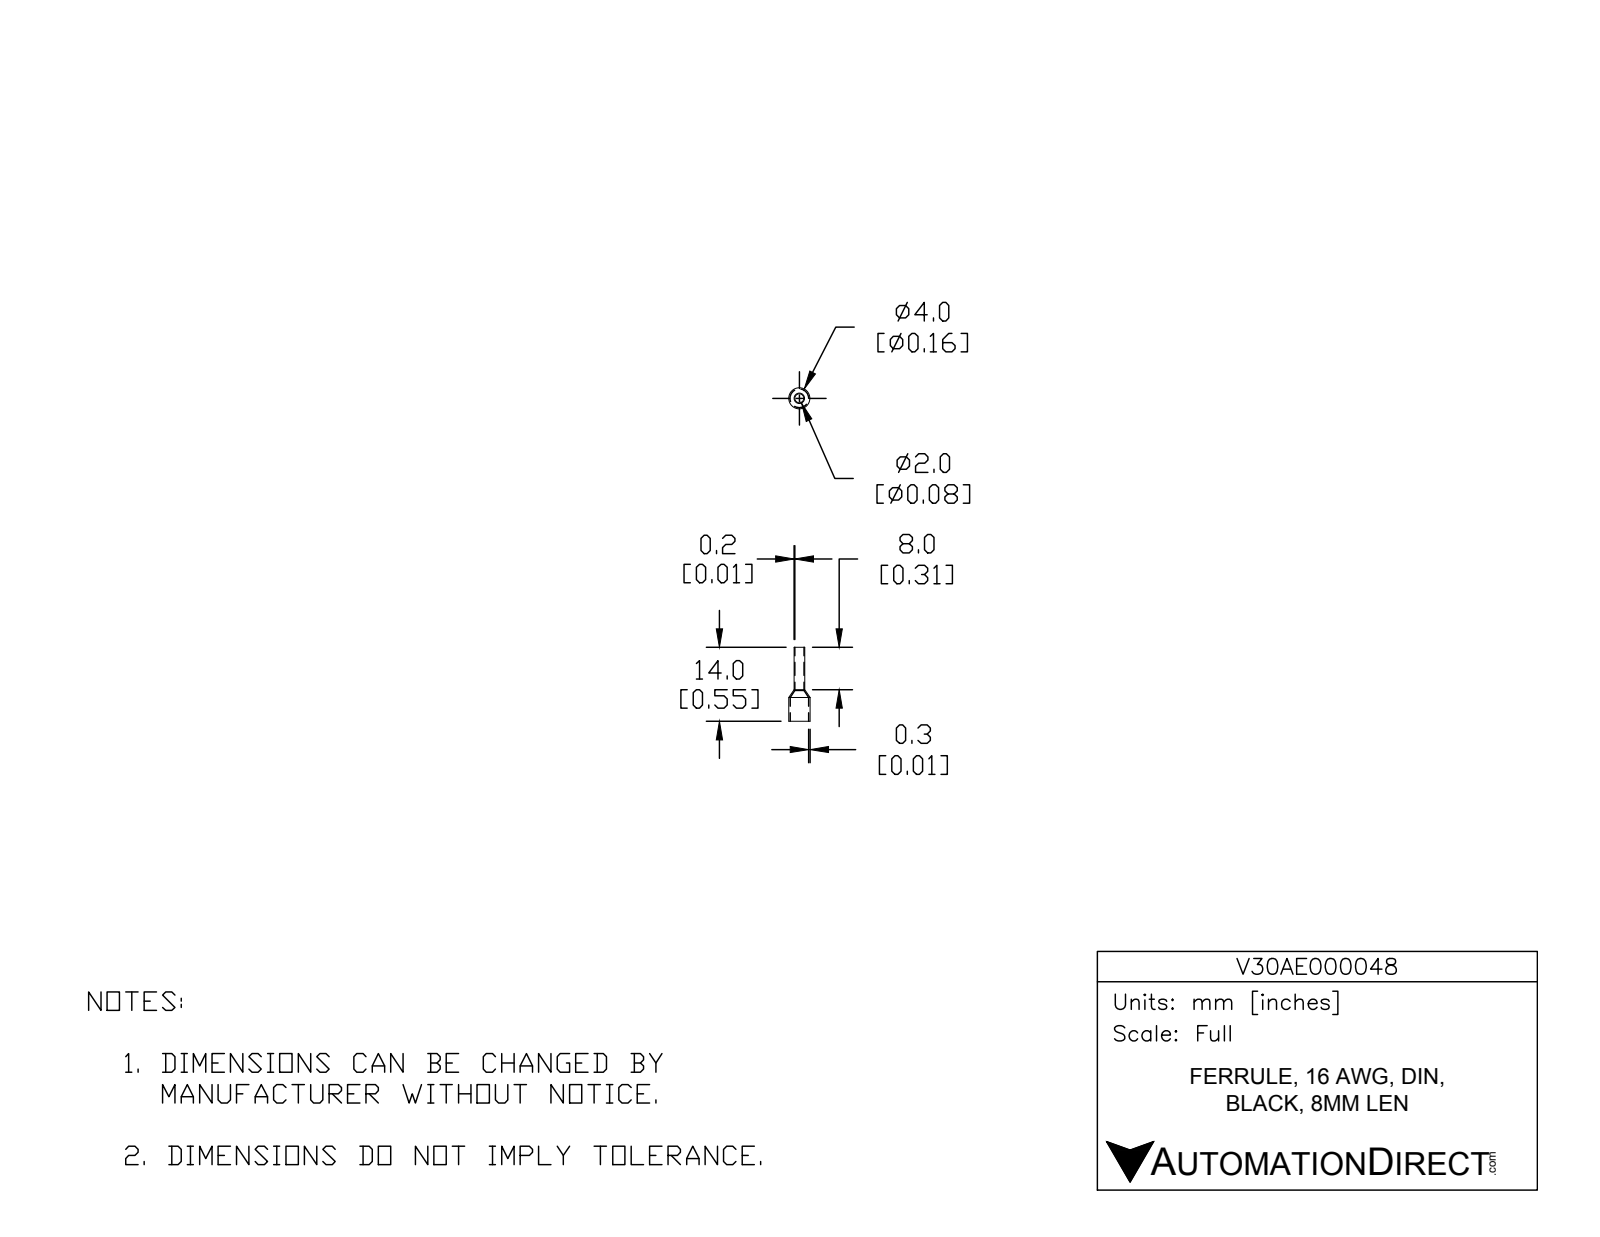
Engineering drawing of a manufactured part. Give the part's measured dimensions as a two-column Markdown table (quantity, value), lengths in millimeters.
| quantity | value |
| --- | --- |
| part name | V30AE000048 |
| STEP written by | SolidWorks 2017 (AUTOMOTIVE_DESIGN) |
| units | millimeters |
| bodies | 1 solid, 14 faces (2 planar, 8 cylindrical, 4 other) |
| overall size | 14 × 4 × 4 |
| volume | 23 mm³ |
| surface area | 234 mm² |
| round holes (diameter × count) | 1.7 × 1, 3.5 × 1 |
| round bosses / shafts (diameter × count) | 4 × 1, 2 × 1 |
| main face-to-face distances | 14 |
